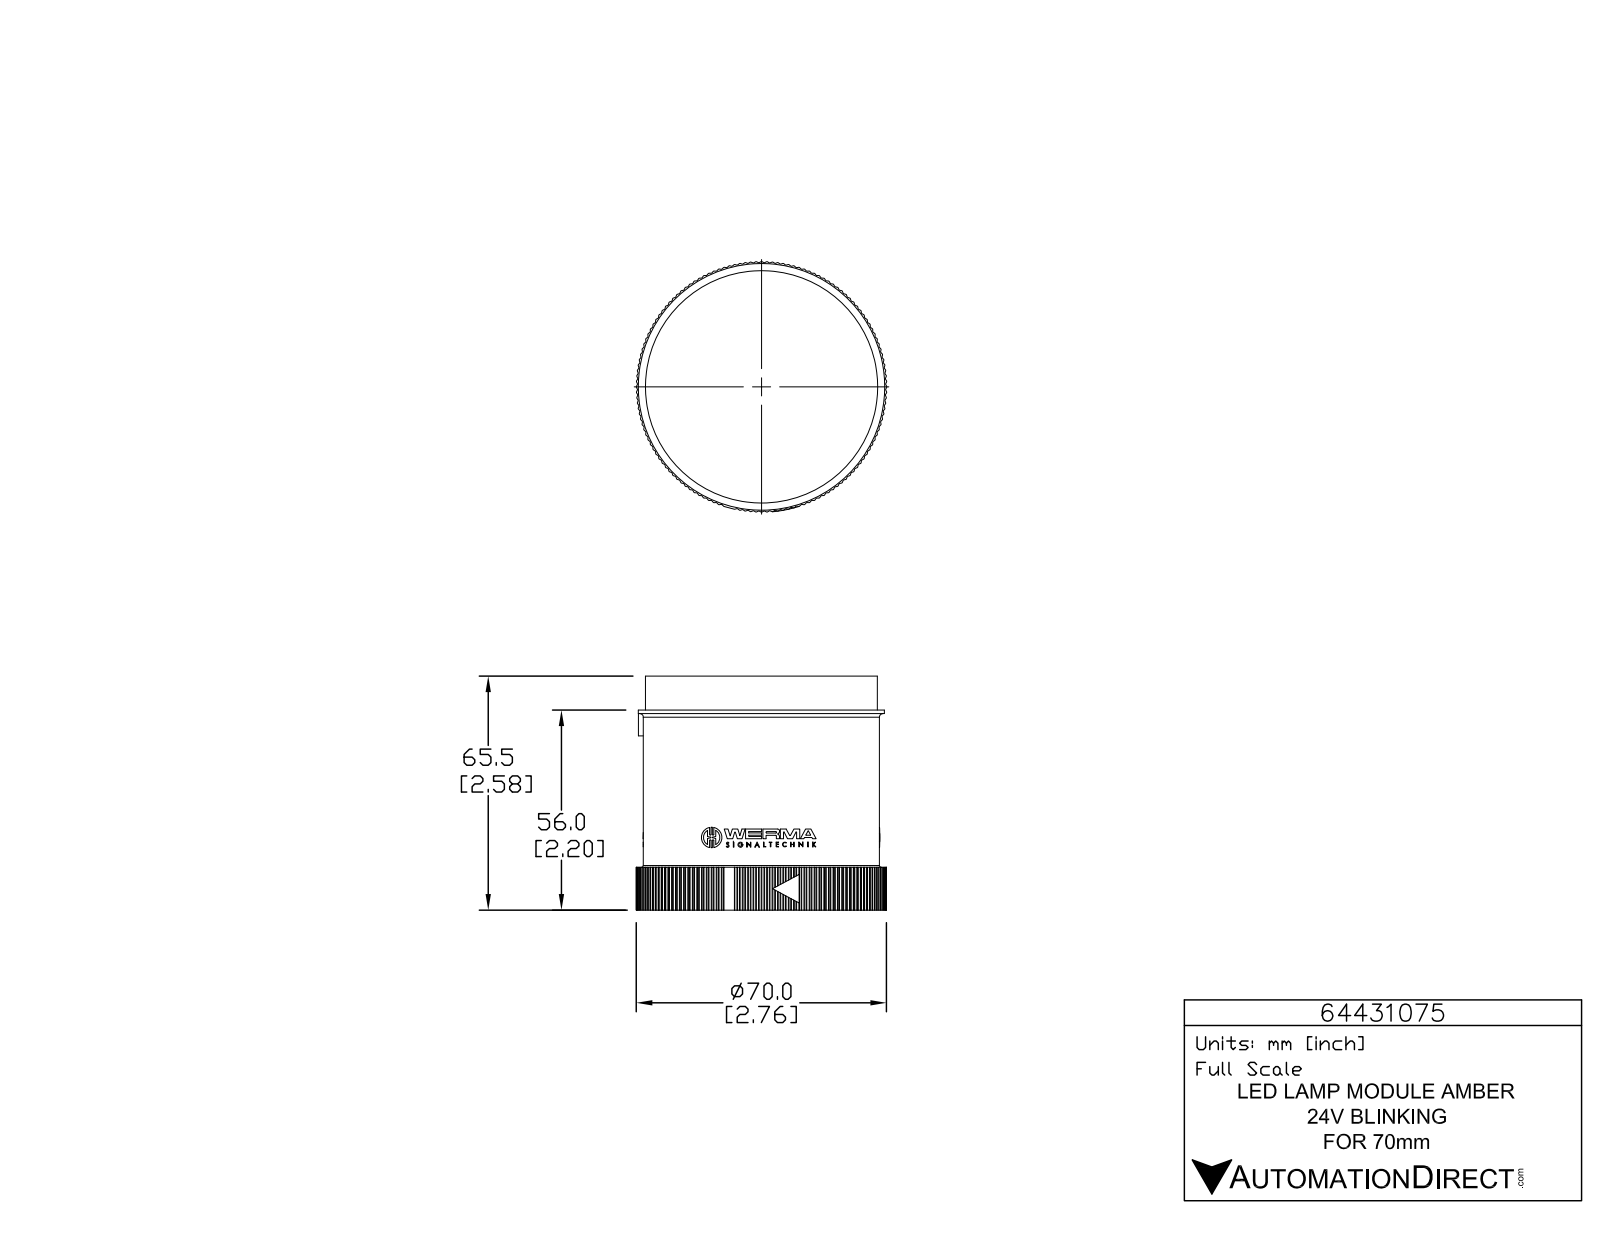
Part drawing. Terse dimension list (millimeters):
name: 64431075
written by: SolidWorks 2015 (AUTOMOTIVE_DESIGN)
unit: mm
bodies: 1 solid, 1400 faces (832 planar, 563 cylindrical, 5 other)
size: 70.2 × 70.2 × 65.5
volume: 197 000 mm³; area: 24 180 mm²
holes: 3× ⌀1, 1× ⌀65.4
bosses: 3× ⌀5.7, 3× ⌀1.4, 1× ⌀69, 1× ⌀66.2, 1× ⌀65
rounds: 285× R0.2, 6× R0.2, 6× R0.2, 6× R0.2, 6× R3.3, 3× R0.1, 3× R0.1, 3× R0.2
face distances: 55.9, 62.3, 9.6, 65.5, 56, 46.4, 9.5, 62.3, 12, 2.4
